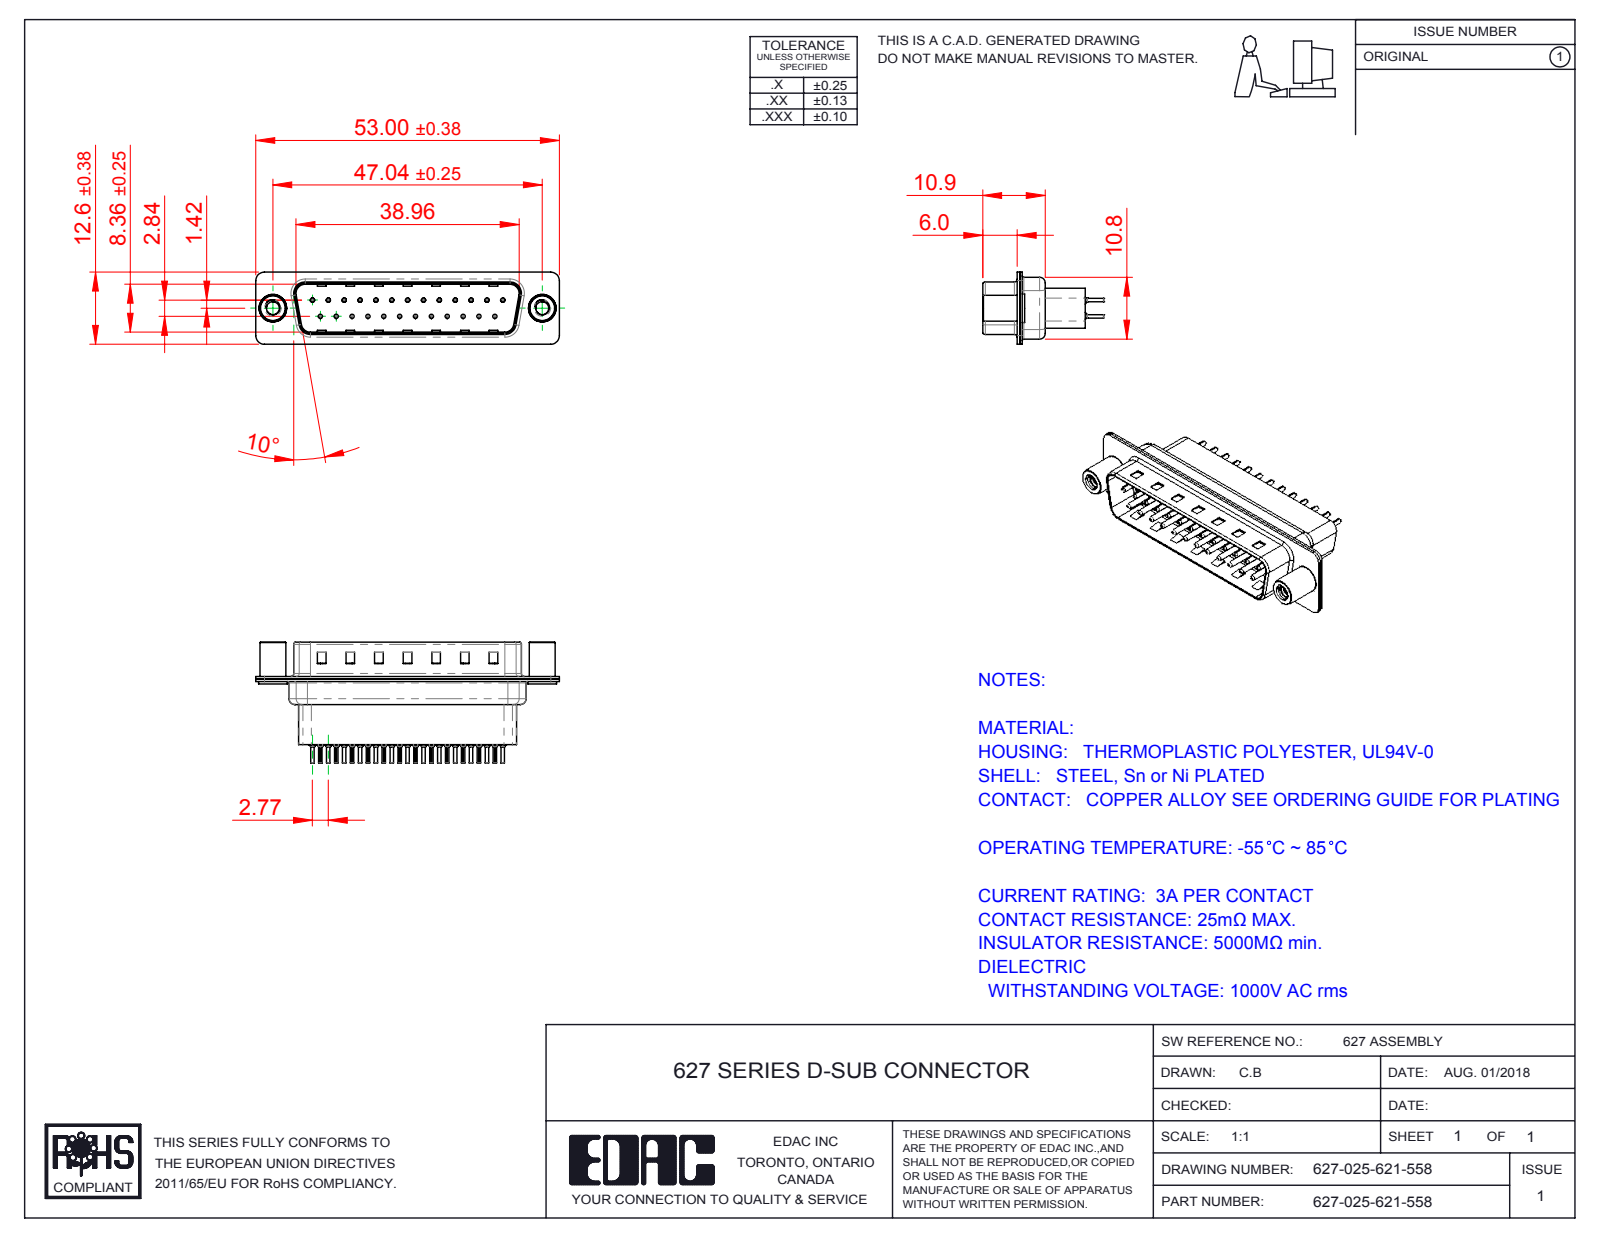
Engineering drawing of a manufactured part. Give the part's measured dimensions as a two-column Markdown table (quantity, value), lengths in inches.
| quantity | value |
| --- | --- |
| part name | 627 4-40 Threaded Standoff; 627-025-621-558; 627 Contact Row 1_21H; 627 Contact Row 2_21H (+3 more) |
| STEP written by | SolidWorks 2016 (CONFIG_CONTROL_DESIGN) |
| units | inches |
| bodies | 30 solids, 2860 faces (773 planar, 1090 cylindrical, 997 other) |
| overall size | 2.087 × 0.831 × 0.496 |
| volume | 0.243 in³ |
| surface area | 15.77 in² |
| round holes (diameter × count) | 0.008 × 25, 0.014 × 25, 0.043 × 25, 0.063 × 25, 0.089 × 2, 0.157 × 2, 0.189 × 2 |
| round bosses / shafts (diameter × count) | 0.079 × 25, 0.059 × 25, 0.03 × 25, 0.024 × 25, 0.197 × 2, 0.193 × 2, 0.177 × 2 |
| partial cylindrical surfaces (radius × count) | 0.004 × 50, 0.059 × 16, 0.079 × 12, 0.02 × 8, 0.063 × 8, 0.01 × 4, 0.024 × 4, 0.026 × 4 |
| main face-to-face distances | 0.016, 0.018, 0.032, 0.377, 0.027, 0.302, 0.035, 0.059, 0.043, 0.318 |
| hole center spacings | 0.124, 0.327, 0.109, 0.218, 0.436, 0.654, 0.198, 0.198 |
